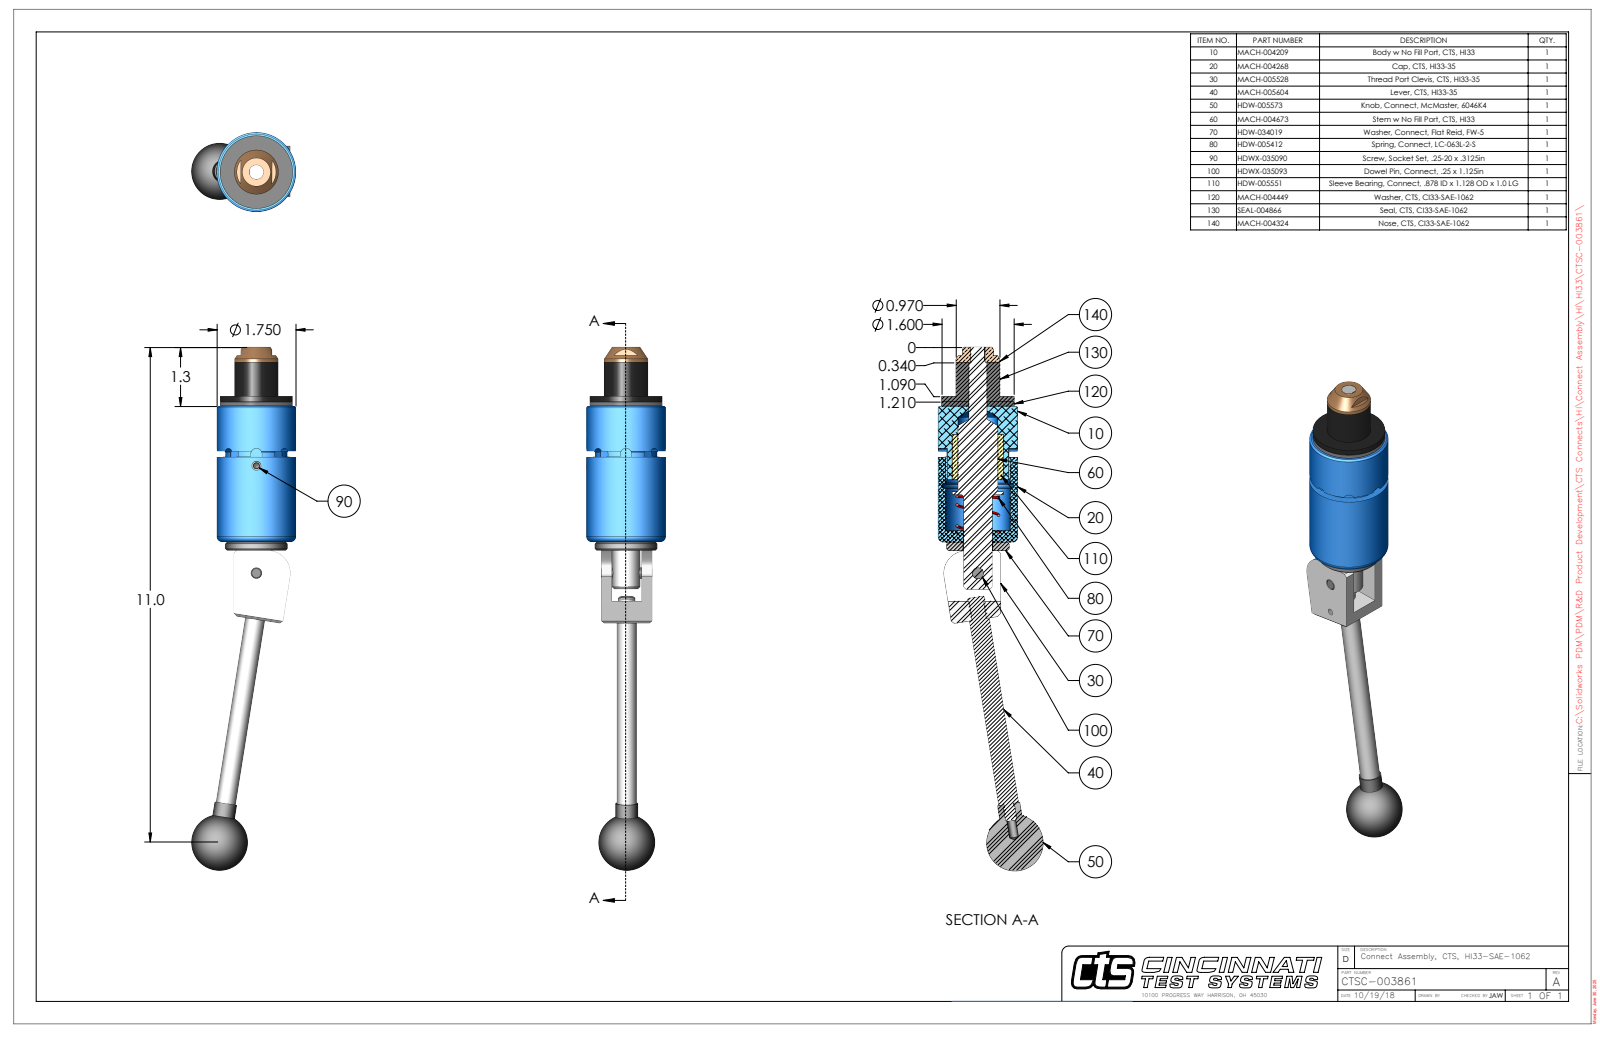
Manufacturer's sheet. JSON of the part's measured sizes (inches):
{"part_name": "CTSC-003861", "step_written_by": "SolidWorks 2023 (AUTOMOTIVE_DESIGN)", "units": "inches", "bodies": {"solids": 9, "faces": 264, "planar": 101, "cylindrical": 104, "other": 59}, "overall_size": [11.591, 2.312, 1.75], "volume_in3": 11.63, "surface_area_in2": 69.84, "round_holes": [[0.201, 2], [0.313, 2], [0.15, 1], [0.249, 1], [0.251, 1], [0.39, 1], [0.397, 1], [0.403, 1], [0.635, 1], [0.656, 1]], "round_bosses_or_shafts": [[0.312, 2], [0.25, 2], [1.75, 1], [1.6, 1], [1.38, 1], [0.97, 1], [0.625, 1], [0.5, 1]], "partial_cylinders_radius": [[0.125, 4], [0.029, 2], [0.5, 1], [0.695, 1], [0.709, 1], [0.744, 1], [0.83, 1]], "face_to_face_distances": [0.098, 3.106, 3.008, 1.12, 3.196, 3.294, 0.188, 0.87, 0.968, 3.976], "hole_center_spacings": [0.74, 2.376, 3.116]}
